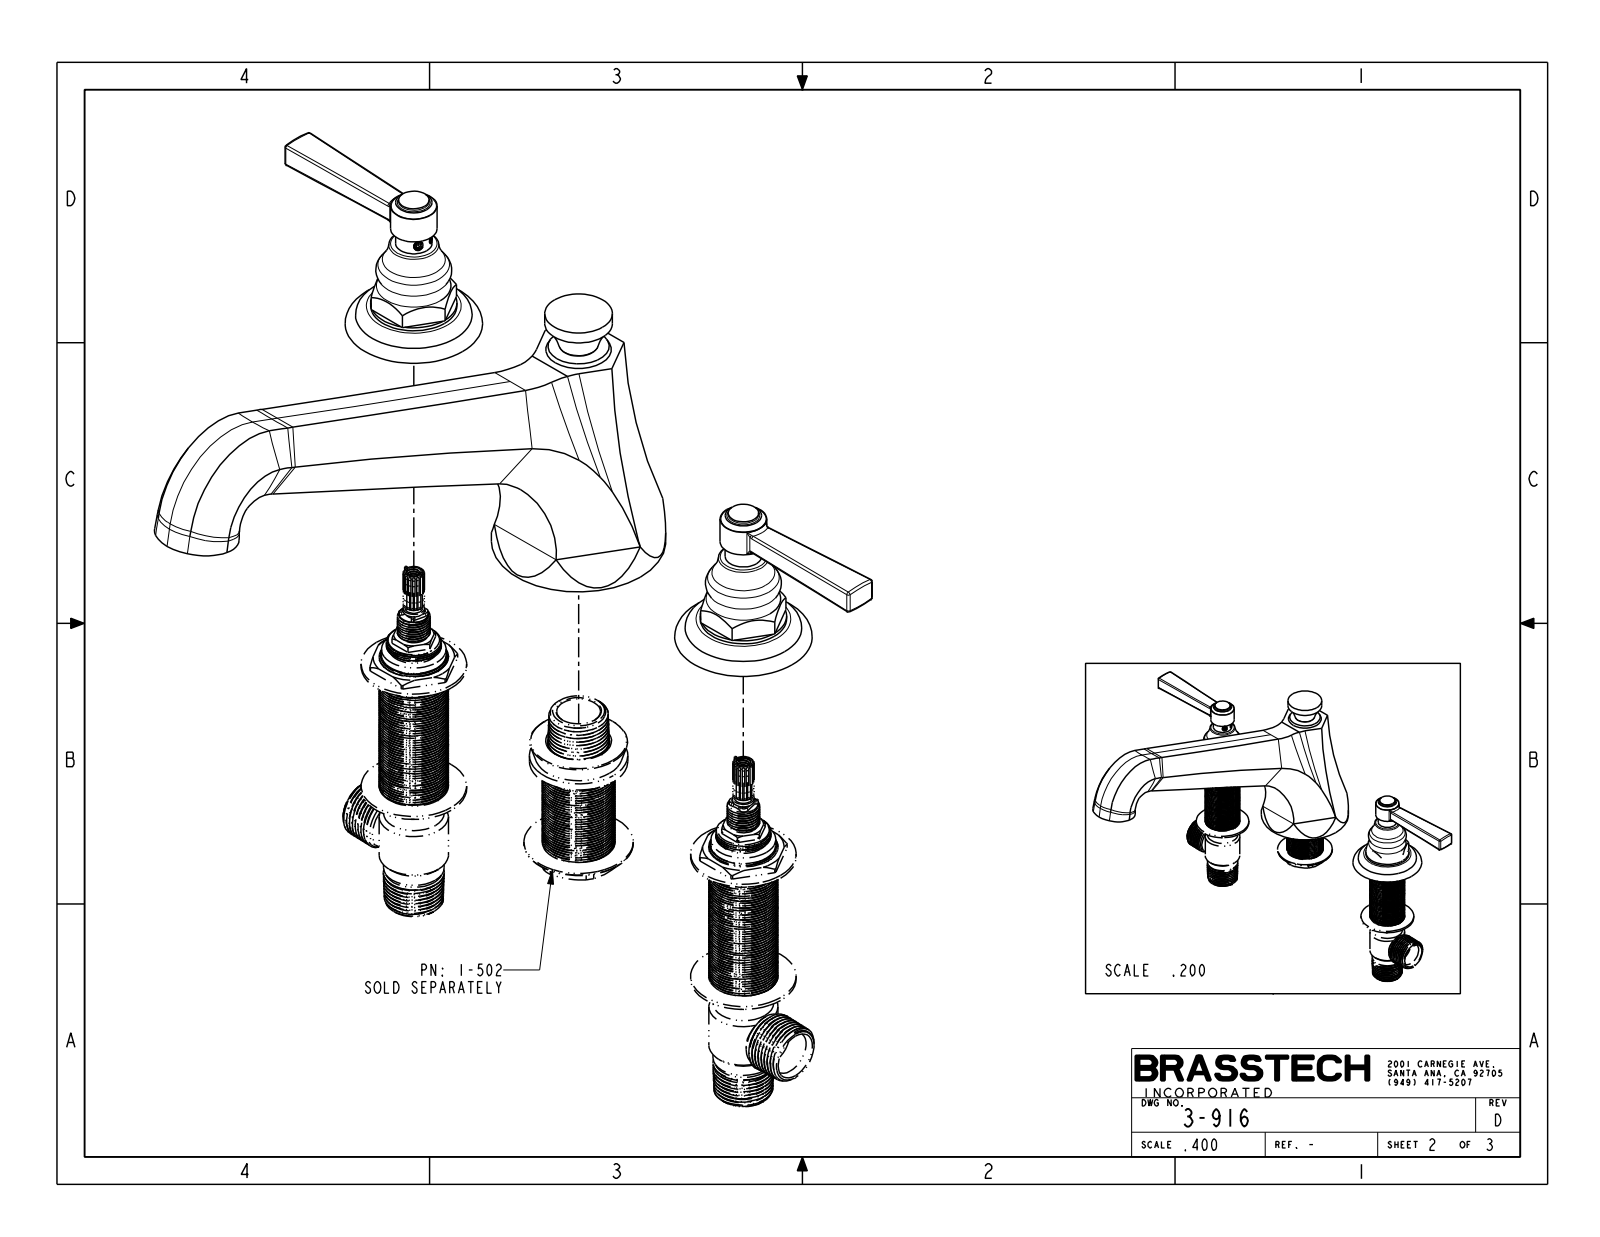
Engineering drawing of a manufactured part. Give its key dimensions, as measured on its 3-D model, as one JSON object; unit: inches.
{"part_name": "3-916", "step_written_by": "CREO PARAMETRIC BY PTC INC, 2018400 (CONFIG_CONTROL_DESIGN)", "units": "inches", "bodies": {"solids": 4, "faces": 265, "planar": 63, "cylindrical": 39, "other": 163}, "overall_size": [13.7, 11.484, 6.573], "volume_in3": 40.76, "surface_area_in2": 131.2, "round_bosses_or_shafts": [[1.482, 2], [0.8, 2], [0.625, 2], [0.525, 2], [0.4, 2], [2.99, 1], [1.16, 1]], "partial_cylinders_radius": [[13, 6], [0.04, 4], [0.055, 4], [2.75, 1]], "face_to_face_distances": [0.12, 6.928, 1.313, 4.115, 1.687, 2.428, 4.045, 2.358, 0.07, 0.375]}
